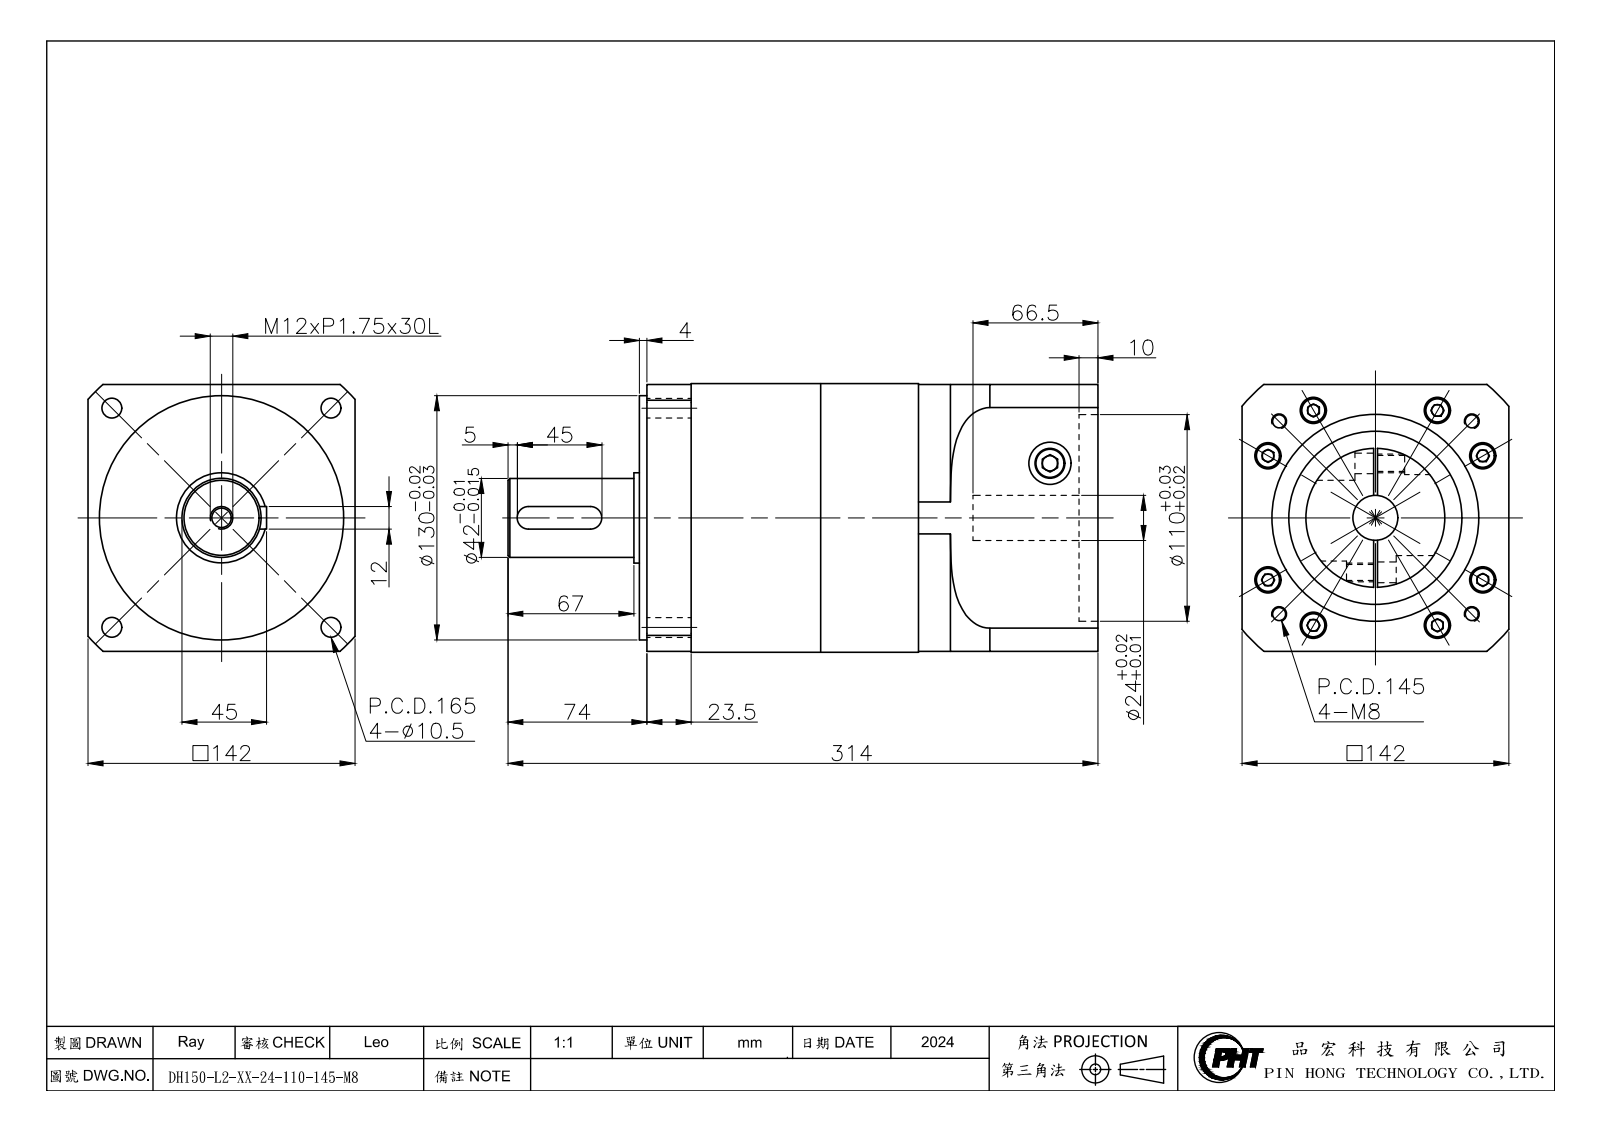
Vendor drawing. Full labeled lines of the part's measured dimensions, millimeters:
Part name (STEP PRODUCT): DH150-L2-XX-24-110-145-M8_2024
STEP written by: SolidWorks 2016 (CONFIG_CONTROL_DESIGN)
Units: millimetres
Bodies: 5 solids, 268 faces (125 planar, 111 cylindrical, 32 other)
Overall size (bounding box): 314 × 143 × 143
Volume: 4 016 000 mm³ · Surface area: 323 527 mm²
Round holes (diameter × count): ⌀9 ×8, ⌀14 ×8, ⌀6.8 ×4, ⌀10.5 ×4, ⌀22.5 ×2, ⌀10.2 ×1, ⌀24 ×1, ⌀42 ×1, ⌀92 ×1, ⌀110 ×1
Round bosses / shafts (diameter × count): ⌀13 ×8, ⌀143 ×1, ⌀130 ×1, ⌀74 ×1, ⌀48 ×1
Partial cylindrical surfaces — rounded edges, fillets, slot ends (radius × count): R6 ×2, R72 ×1, R92.5 ×1, R95 ×1
Main face-to-face distances: 69, 142, 96.5, 27.5, 147.5, 216.5, 244, 4, 70, 240
Hole centre spacings: 66, 19.2, 25.37, 84.48, 91.35, 93.34, 109.84, 109.96
